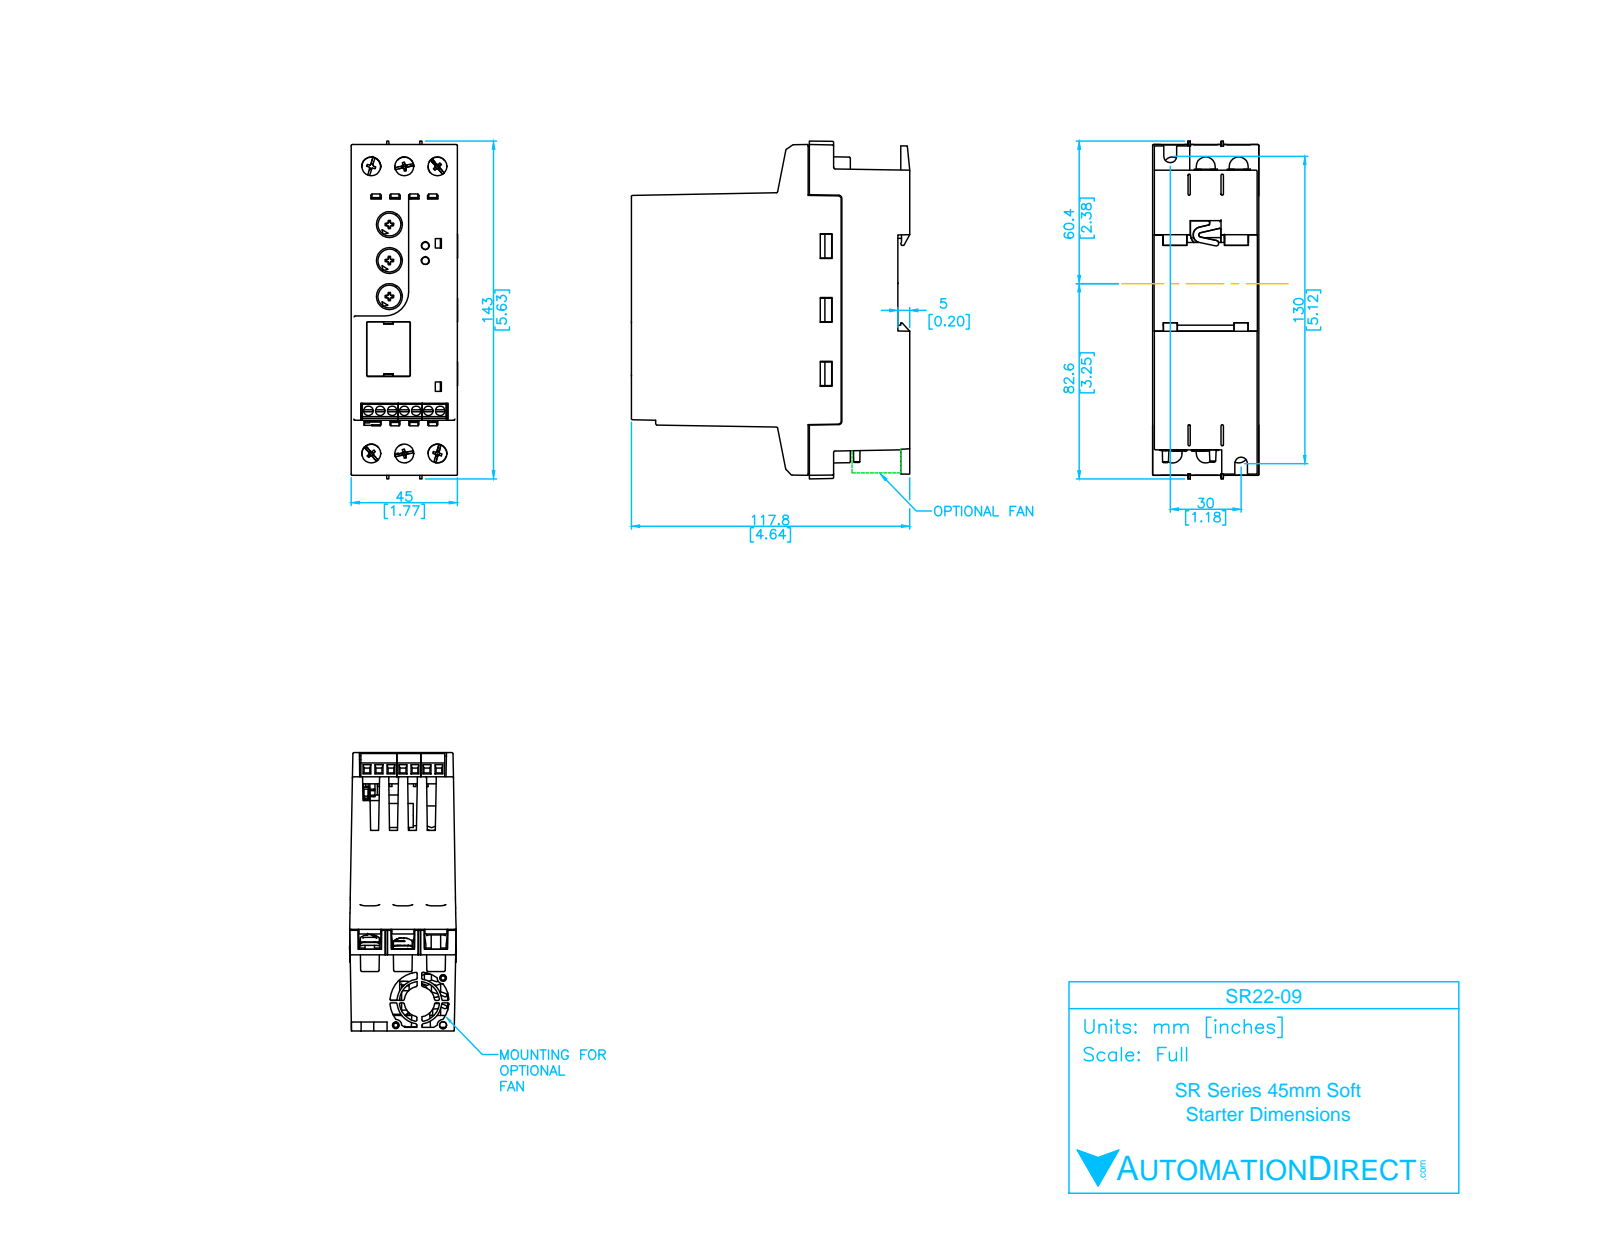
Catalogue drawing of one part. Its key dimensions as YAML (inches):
part_name: "SR22-09"
step_written_by: "SolidWorks 2013 (AUTOMOTIVE_DESIGN)"
units: inches
bodies: {solids: 1, faces: 567, planar: 437, cylindrical: 98, other: 32}
overall_size: [5.669, 4.638, 1.797]
volume: 34.95
surface_area: 86.83
round_holes:
  - {diameter: 0.374, count: 6}
  - {diameter: 0.138, count: 5}
  - {diameter: 0.445, count: 3}
  - {diameter: 0.157, count: 2}
round_bosses_or_shafts:
  - {diameter: 0.411, count: 3}
partial_cylinders:
  - {radius: 0.02, count: 36}
  - {radius: 0.192, count: 6}
  - {radius: 0.039, count: 2}
  - {radius: 0.108, count: 2}
  - {radius: 0.394, count: 1}
face_to_face_distances: [1.772, 1.771, 1.77, 4.638, 0.02, 0.202, 4.435, 0.059, 4.579, 4.376]
hole_center_spacings: [0.207, 0.512, 4.87, 0.413, 4.843, 0.591, 0.62, 1.024]
